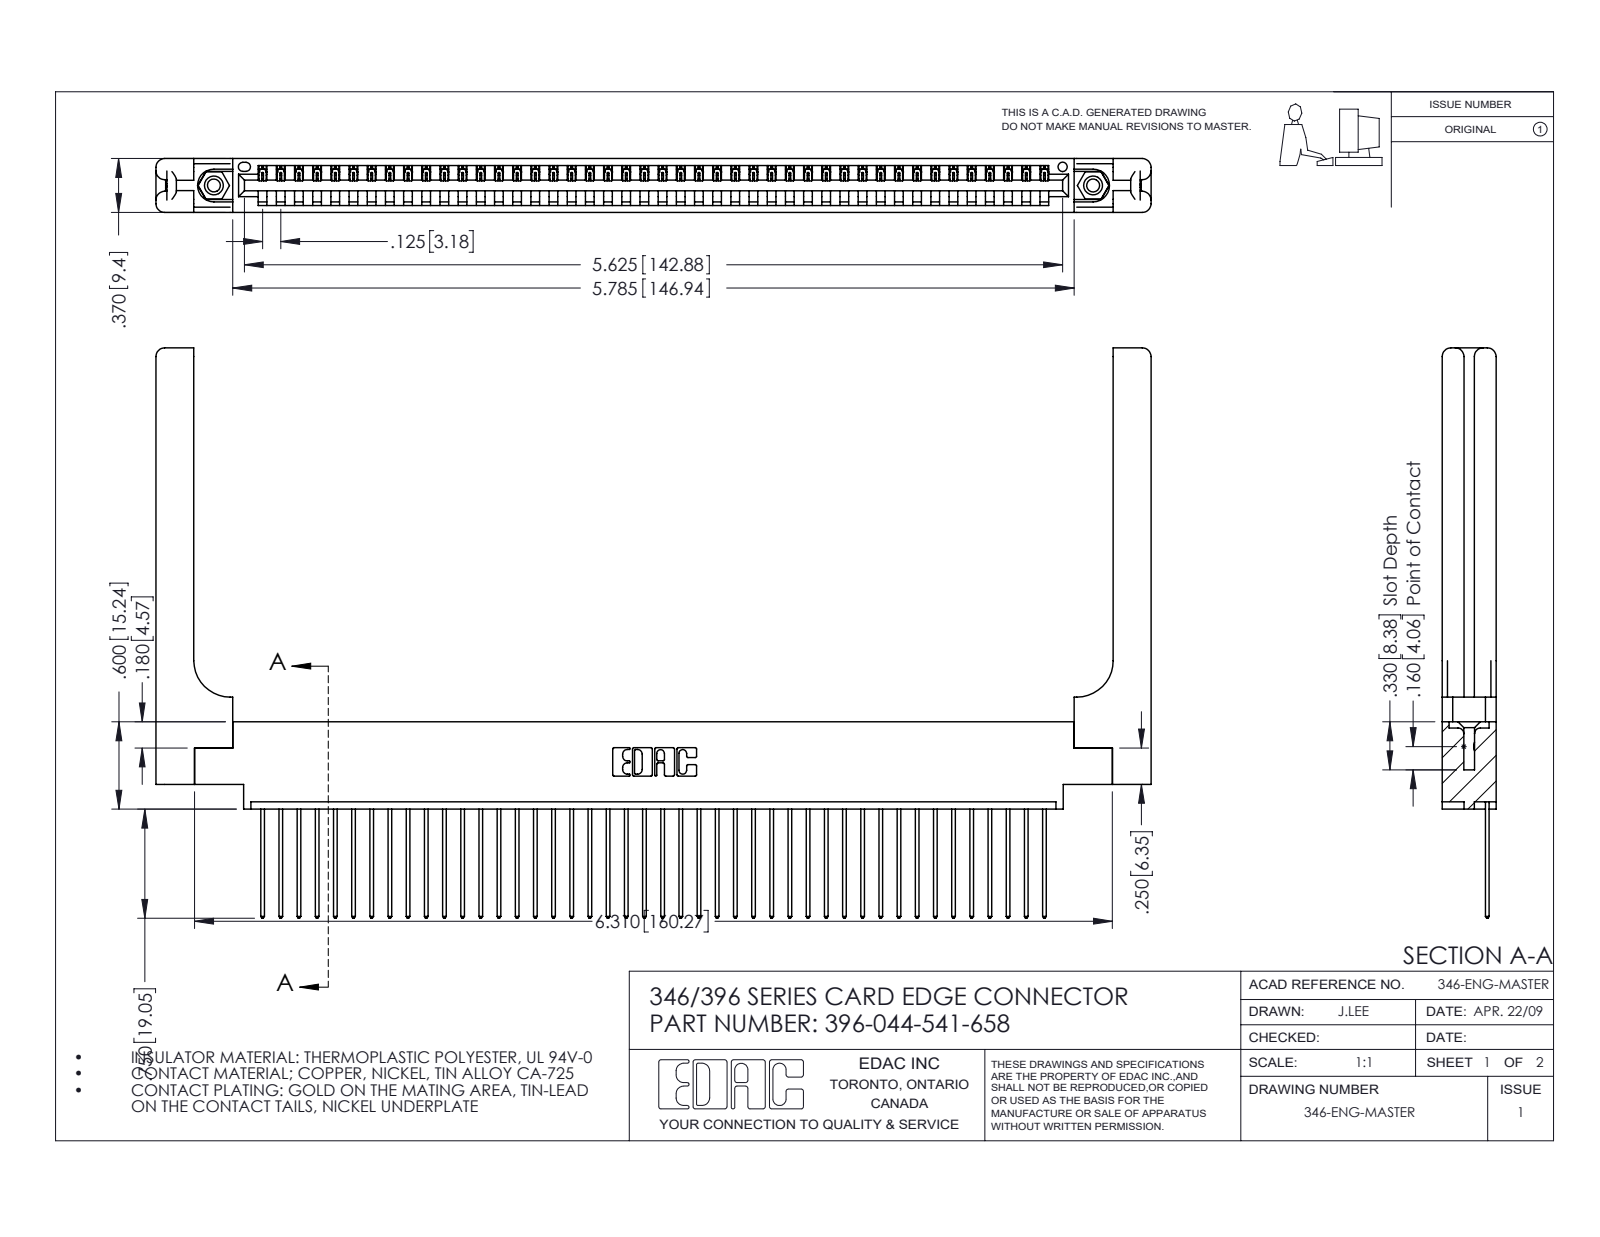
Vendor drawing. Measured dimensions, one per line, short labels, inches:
name: 346 Part_0.170 Offset - 0.156 Dia-TH; 345-292-001_345-293-141; 345-250-001_345-250-001-102; 346-220-058_345-220-058 (+1 more)
written by: SolidWorks 2016 (CONFIG_CONTROL_DESIGN)
unit: in
bodies: 49 solids, 2934 faces (1988 planar, 886 cylindrical, 60 other)
size: 6.841 × 3.92 × 0.37
volume: 1.474 in³; area: 41.87 in²
holes: 2× ⌀0.089, 2× ⌀0.125, 2× ⌀0.156, 1× ⌀0.064
bosses: 2× ⌀0.155
rounds: 88× R0.006, 88× R0.01, 22× R0.01, 16× R0.06, 6× R0.007, 6× R0.031, 3× R0.026, 2× R0.03
face distances: 0.37, 0.048, 0.322, 0.072, 0.148, 0.15, 0.298, 0.025, 0.25, 0.222
hole spacings: 0.246, 5.836, 6.045
